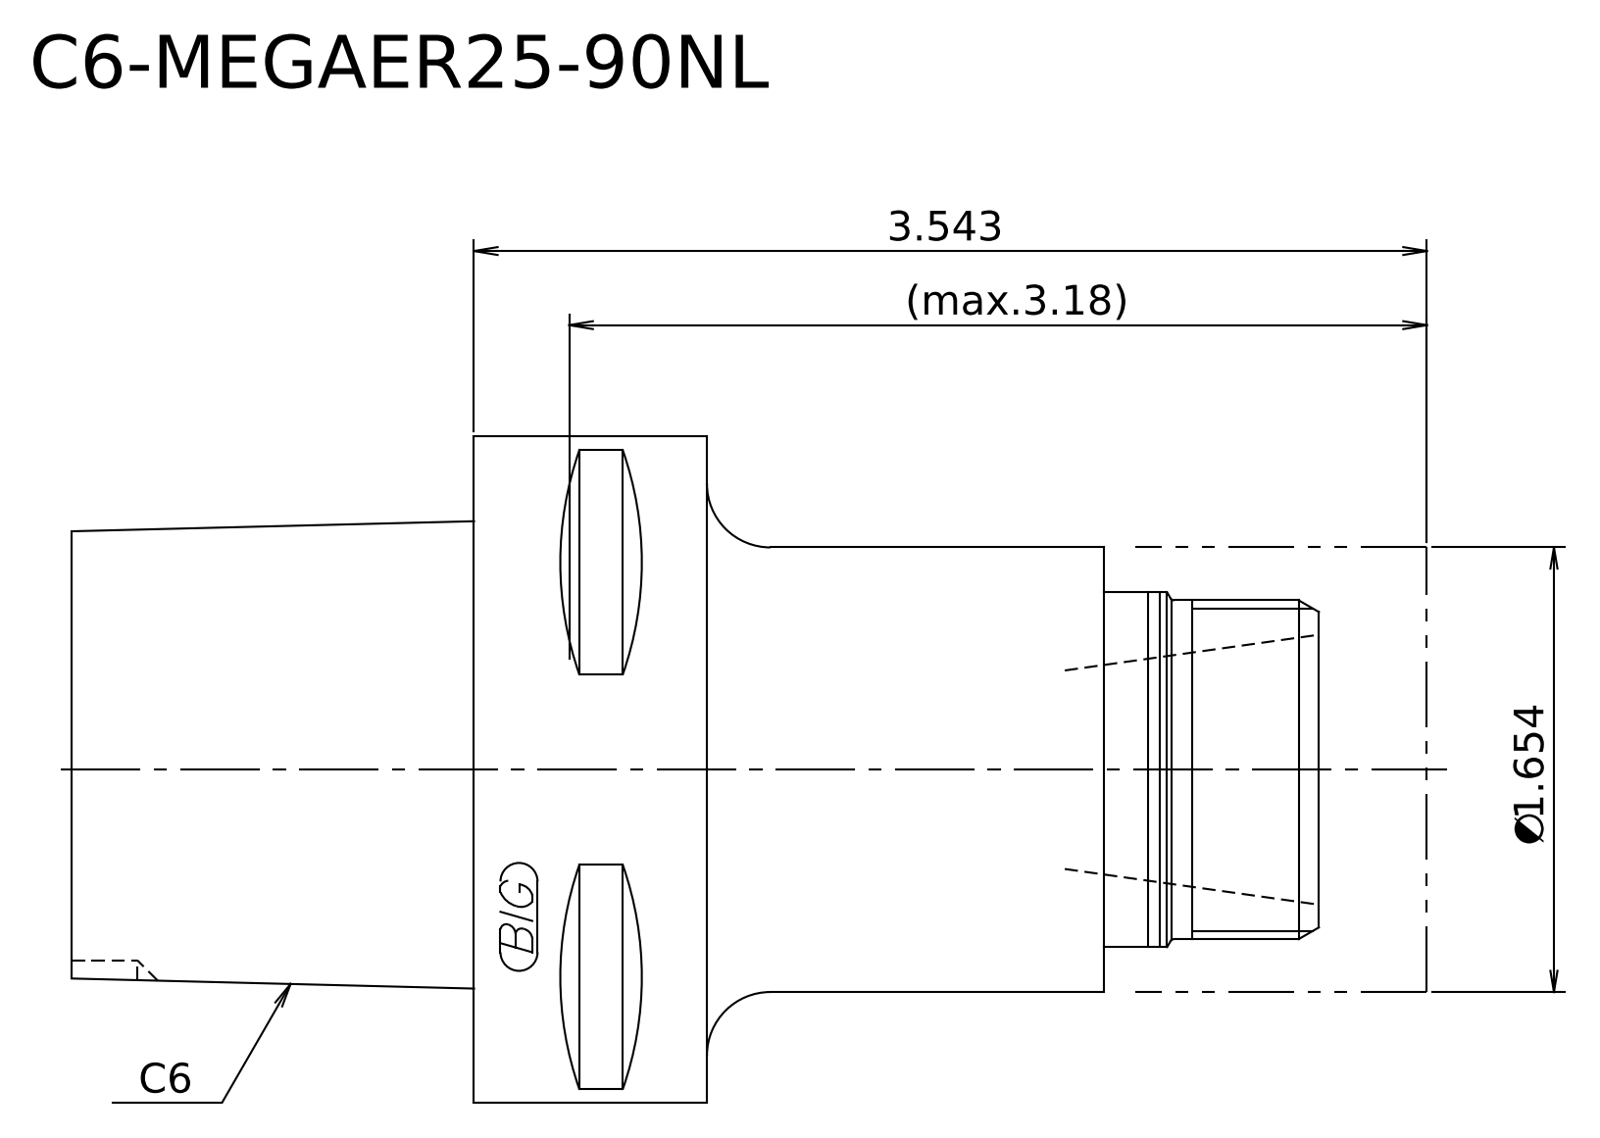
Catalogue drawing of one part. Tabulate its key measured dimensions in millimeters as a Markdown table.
| quantity | value |
| --- | --- |
| STEP written by | Kubotek KeyCreator 2011 V10.0.2 (22737) (automotive_design) |
| units | millimeters |
| bodies | 2 solids, 18 faces (7 planar, 5 cylindrical, 6 other) |
| overall size | 128 × 63 × 63 |
| volume | 232 716 mm³ |
| surface area | 28 501 mm² |
| round bosses / shafts (diameter × count) | 63 × 1, 42 × 1, 33.5 × 1, 32 × 1 |
| main face-to-face distances | 62.5, 27.5, 90, 128, 100.5, 38, 68, 40.5, 22, 60 |
